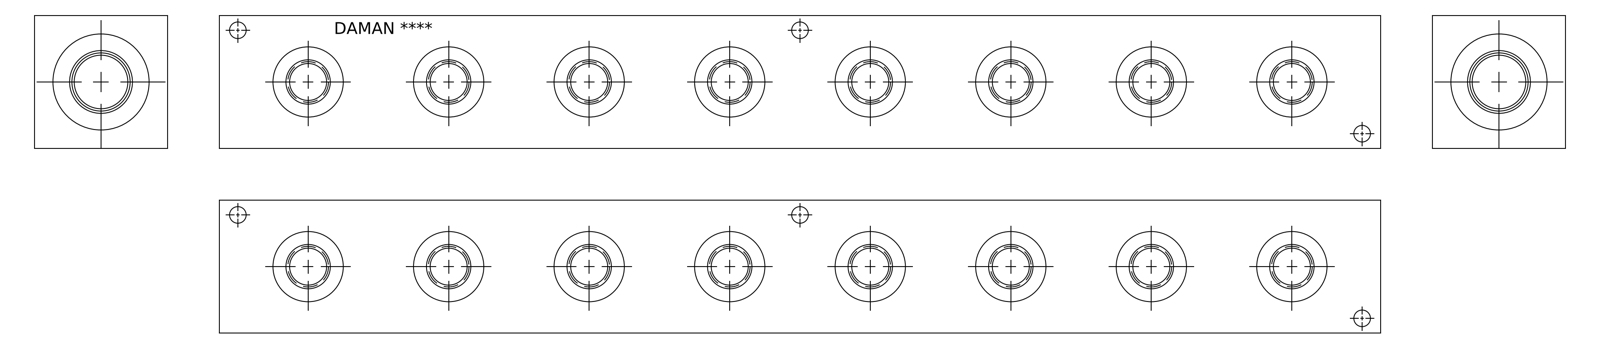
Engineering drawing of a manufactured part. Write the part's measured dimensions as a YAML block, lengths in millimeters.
part_name: "Part_AH0900808S_3D"
step_written_by: "Autodesk Inventor 2019 (AUTOMOTIVE_DESIGN)"
units: millimeters
bodies: {solids: 1, faces: 519, planar: 236, cylindrical: 92, other: 191}
overall_size: [498.48, 57.15, 57.15]
volume: 1480000
surface_area: 151304
round_holes:
  - {diameter: 17.5, count: 16}
  - {diameter: 19.05, count: 16}
  - {diameter: 19.25, count: 16}
  - {diameter: 30.63, count: 16}
  - {diameter: 7.14, count: 6}
  - {diameter: 15.88, count: 6}
  - {diameter: 23.01, count: 1}
  - {diameter: 24.92, count: 1}
  - {diameter: 26.99, count: 1}
  - {diameter: 27.43, count: 1}
  - {diameter: 42.04, count: 1}
face_to_face_distances: [57.15, 0.79, 56.36, 498.48, 497.69, 496.9, 42.09, 14.27, 15.06, 19.84]
hole_center_spacings: [120.65, 60.33, 180.98, 60.32, 241.3, 301.63, 37.48, 93.16]
